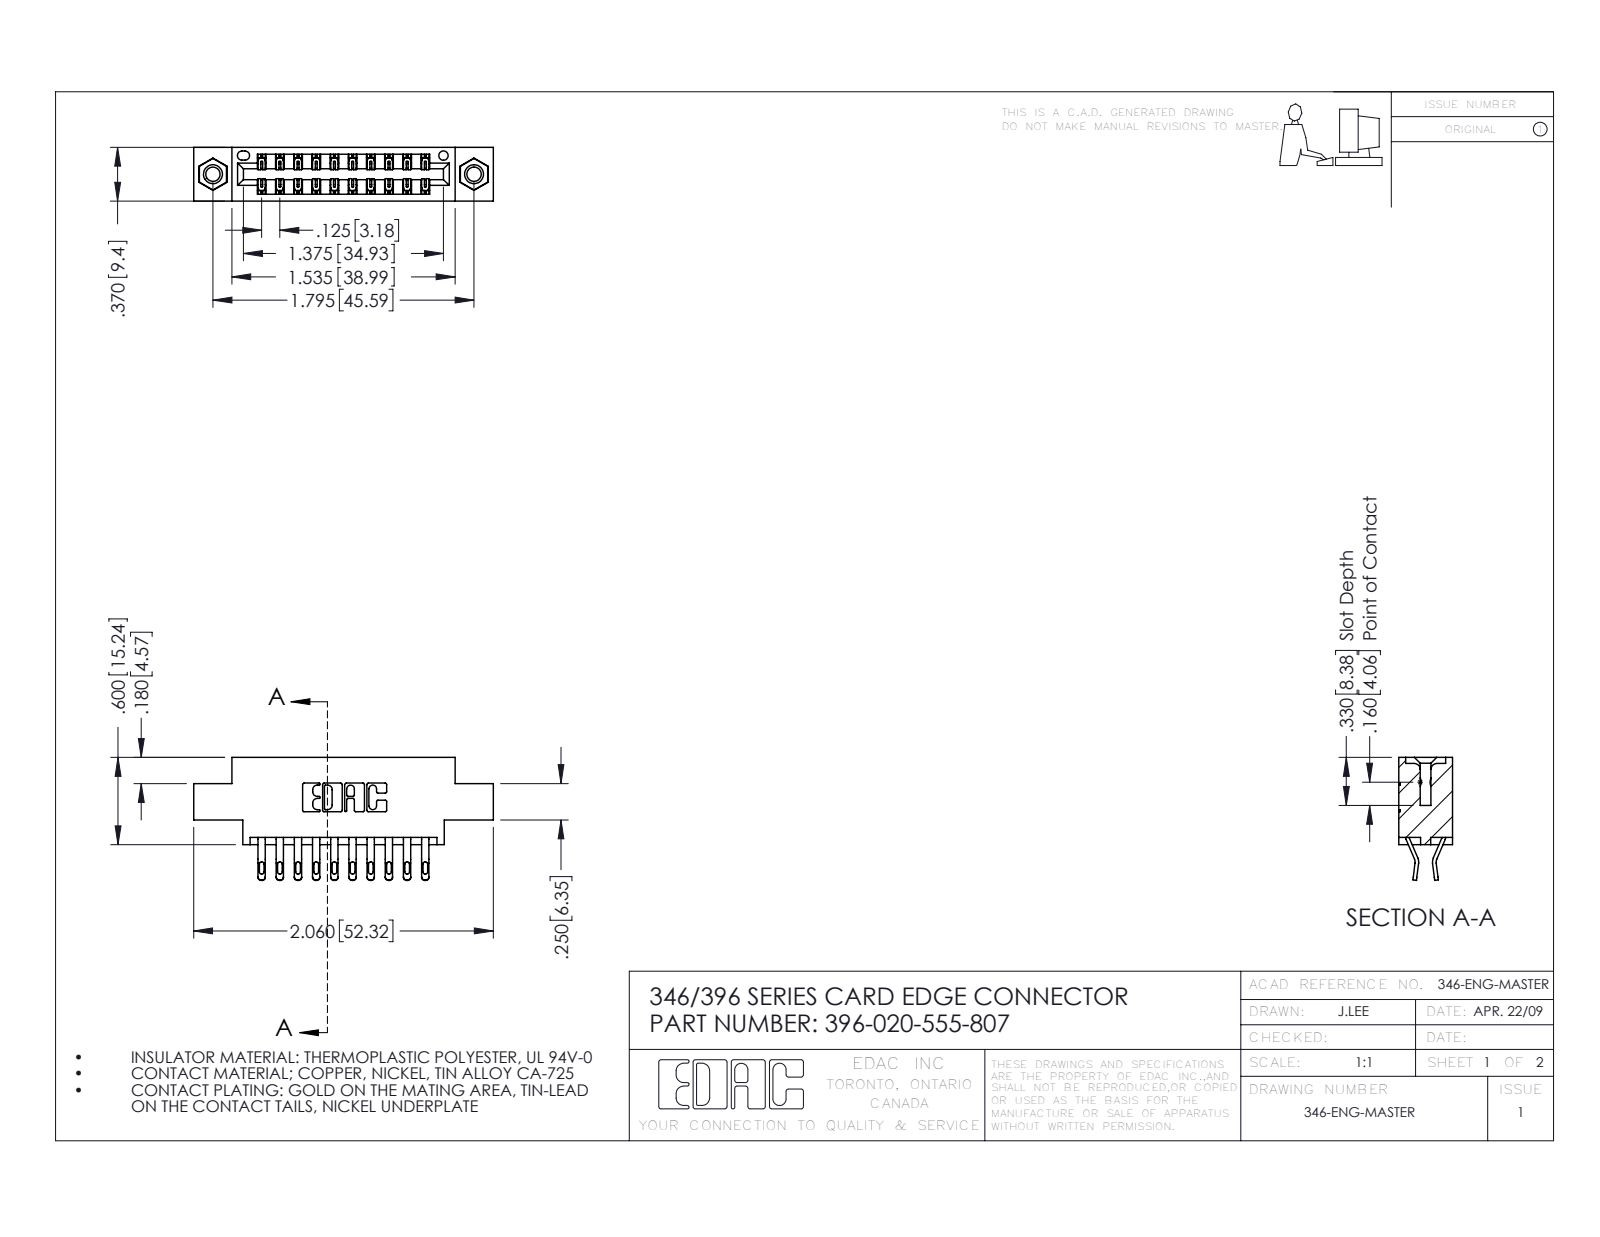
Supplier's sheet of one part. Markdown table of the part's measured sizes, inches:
| quantity | value |
| --- | --- |
| part name | 346 Part_0.170 Offset - 0.156 Dia-TI; 345-250-001_345-250-005-103; 396-020-555-807; 345-292-001_555 Tail |
| STEP written by | SolidWorks 2016 (CONFIG_CONTROL_DESIGN) |
| units | inches |
| bodies | 23 solids, 1346 faces (772 planar, 558 cylindrical, 16 other) |
| overall size | 2.06 × 0.845 × 0.37 |
| volume | 0.289 in³ |
| surface area | 9.978 in² |
| round holes (diameter × count) | 0.098 × 2, 0.125 × 2, 0.156 × 2, 0.064 × 1 |
| round bosses / shafts (diameter × count) | 0.155 × 2 |
| partial cylindrical surfaces (radius × count) | 0.016 × 40, 0.02 × 40, 0.006 × 30, 0.01 × 22, 0.007 × 6, 0.031 × 6, 0.026 × 3, 0.01 × 2 |
| main face-to-face distances | 0.25, 0.37, 0.048, 0.322, 0.222, 0.025, 0.148, 0.072, 0.298, 0.275 |
| hole center spacings | 0.246, 1.59, 1.795 |
